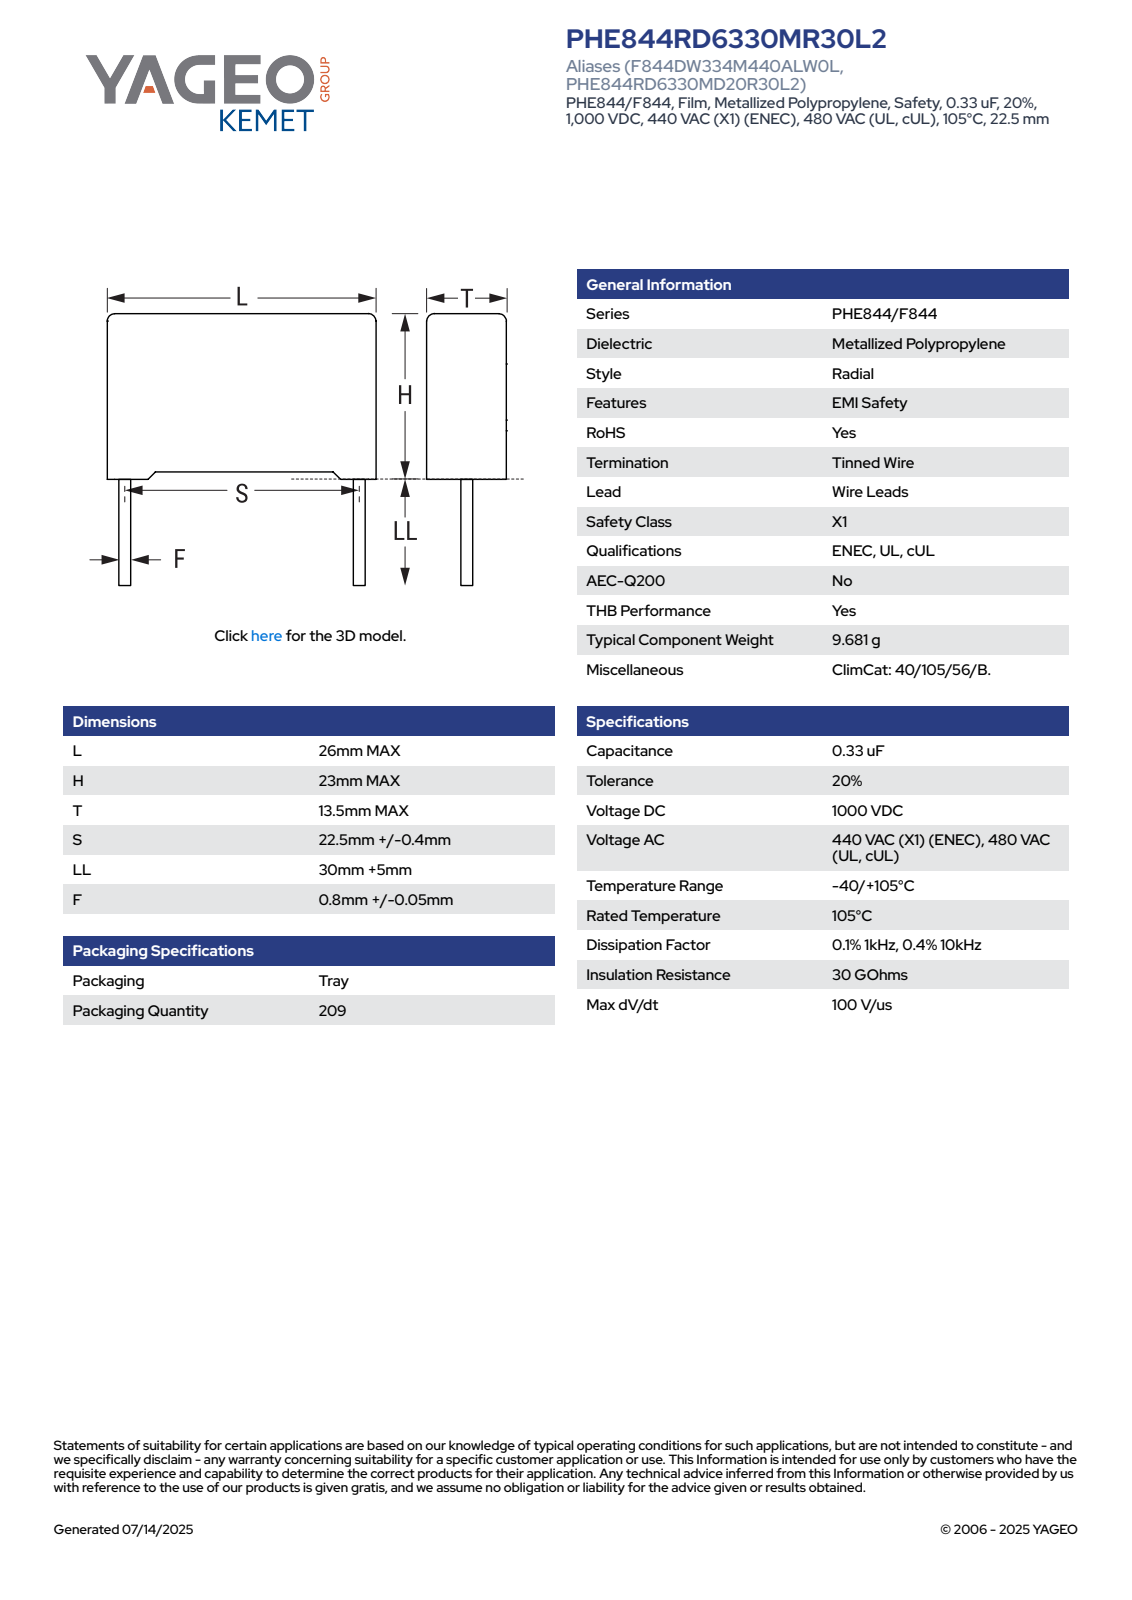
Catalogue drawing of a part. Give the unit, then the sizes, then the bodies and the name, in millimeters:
Units: millimetres
Overall size (bounding box): 58 × 26 × 13.51
Round bosses / shafts (diameter × count): ⌀0.85 ×2
Partial cylindrical surfaces — rounded edges, fillets, slot ends (radius × count): R0.5 ×4
Main face-to-face distances: 13.5, 26, 22.21, 22.25, 0.79, 0.75, 23, 0.87, 25.13, 24.26
Volume: 7 860 mm³ · Surface area: 2 741 mm²
Bodies: 4 solids, 85 faces (77 planar, 8 cylindrical, 0 other)
Part name (STEP PRODUCT): CFR_RB2_26X23X13.5_L26H23T13.5S22.5LL35F0.85
STEP written by: SolidWorks 2021 (AUTOMOTIVE_DESIGN)
